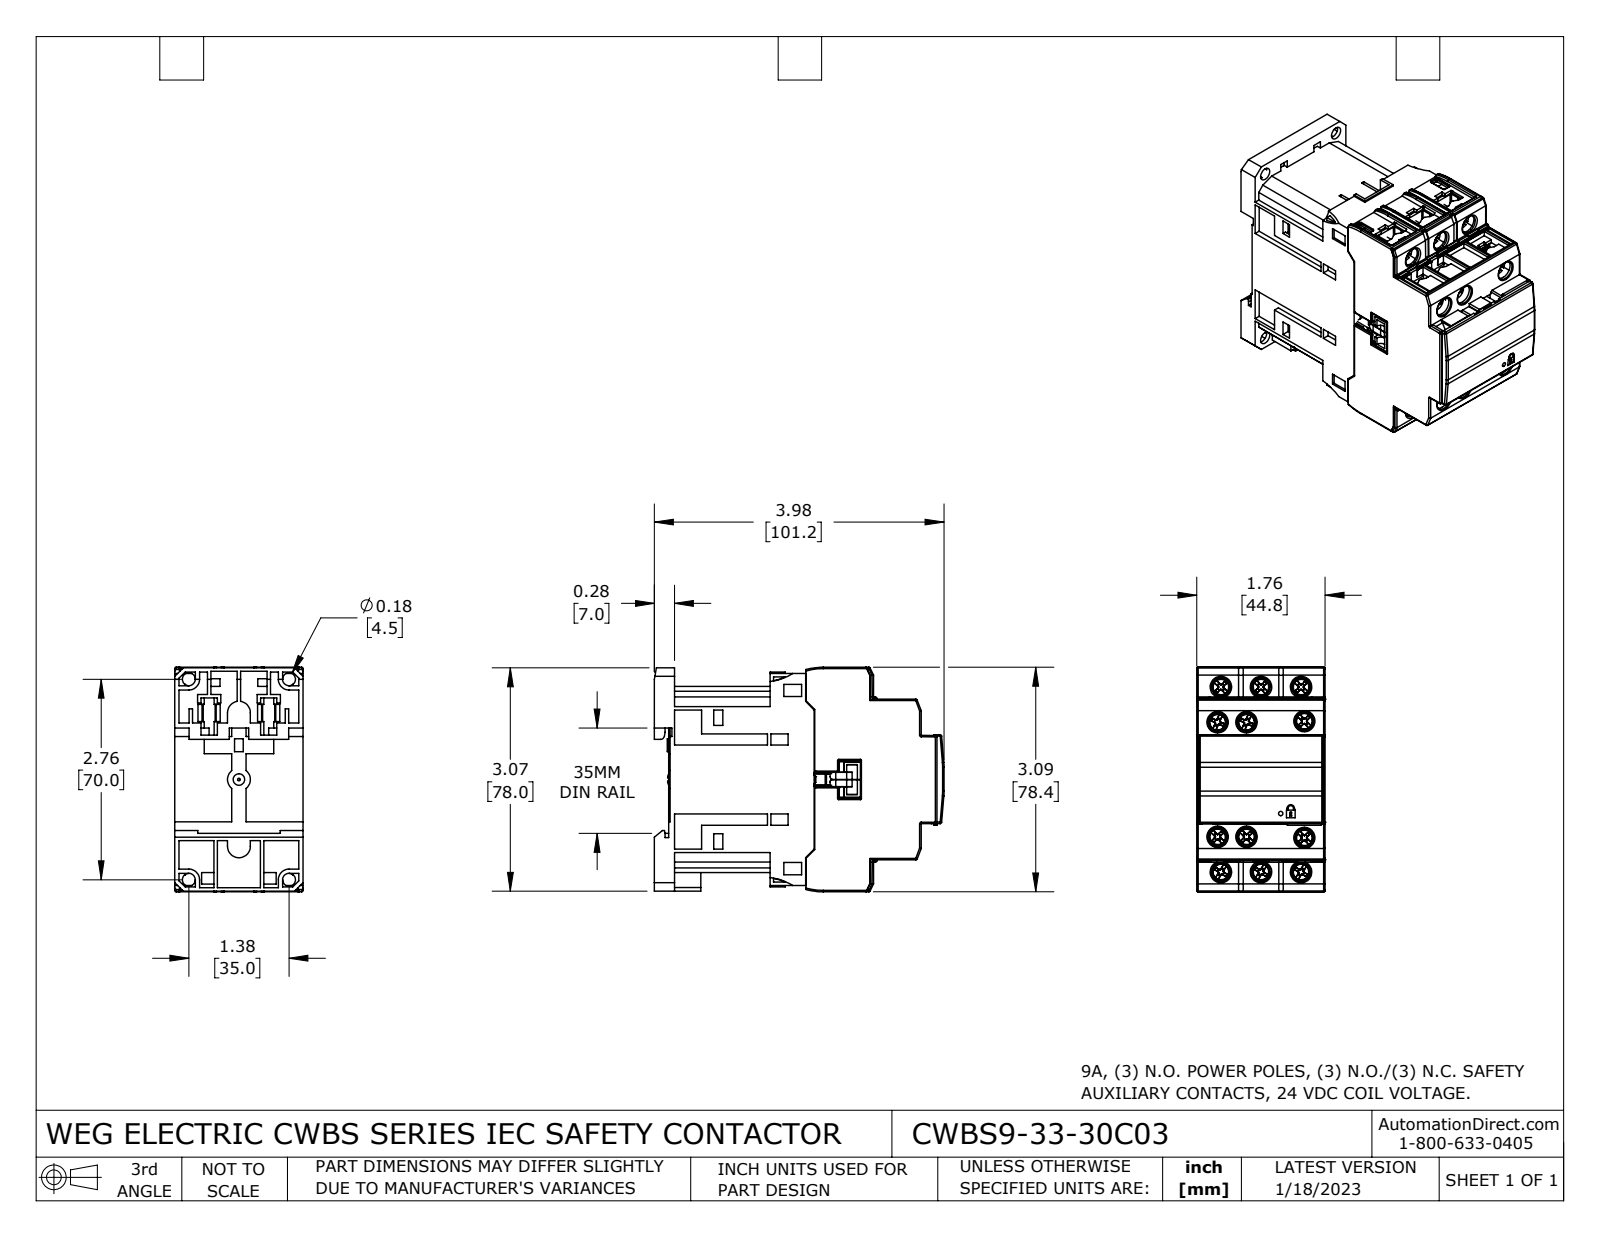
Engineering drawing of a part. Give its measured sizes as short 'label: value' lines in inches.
name: CWBS9-33-30C03
written by: SolidWorks 2021 (CONFIG_CONTROL_DESIGN)
unit: in
bodies: 45 solids, 3244 faces (2306 planar, 594 cylindrical, 344 other)
size: 3.982 × 3.087 × 1.764
volume: 15.16 in³; area: 128.7 in²
holes: 12× ⌀0.124, 6× ⌀0.256, 4× ⌀0.177, 2× ⌀0.236, 1× ⌀0.059
bosses: 12× ⌀0.169, 12× ⌀0.138, 8× ⌀0.107, 4× ⌀0.107
rounds: 134× R0.02, 52× R0.012, 24× R0.071, 24× R0.964, 24× R2.128, 20× R0.016, 17× R0.039, 11× R0.106
face distances: 1.764, 0.047, 3.667, 1.717, 1.687, 0.028, 0.157, 1.53, 1.98, 2.138
hole spacings: 0.551, 1.102, 0.829, 2.396, 0.237, 0.398, 0.584, 0.598
